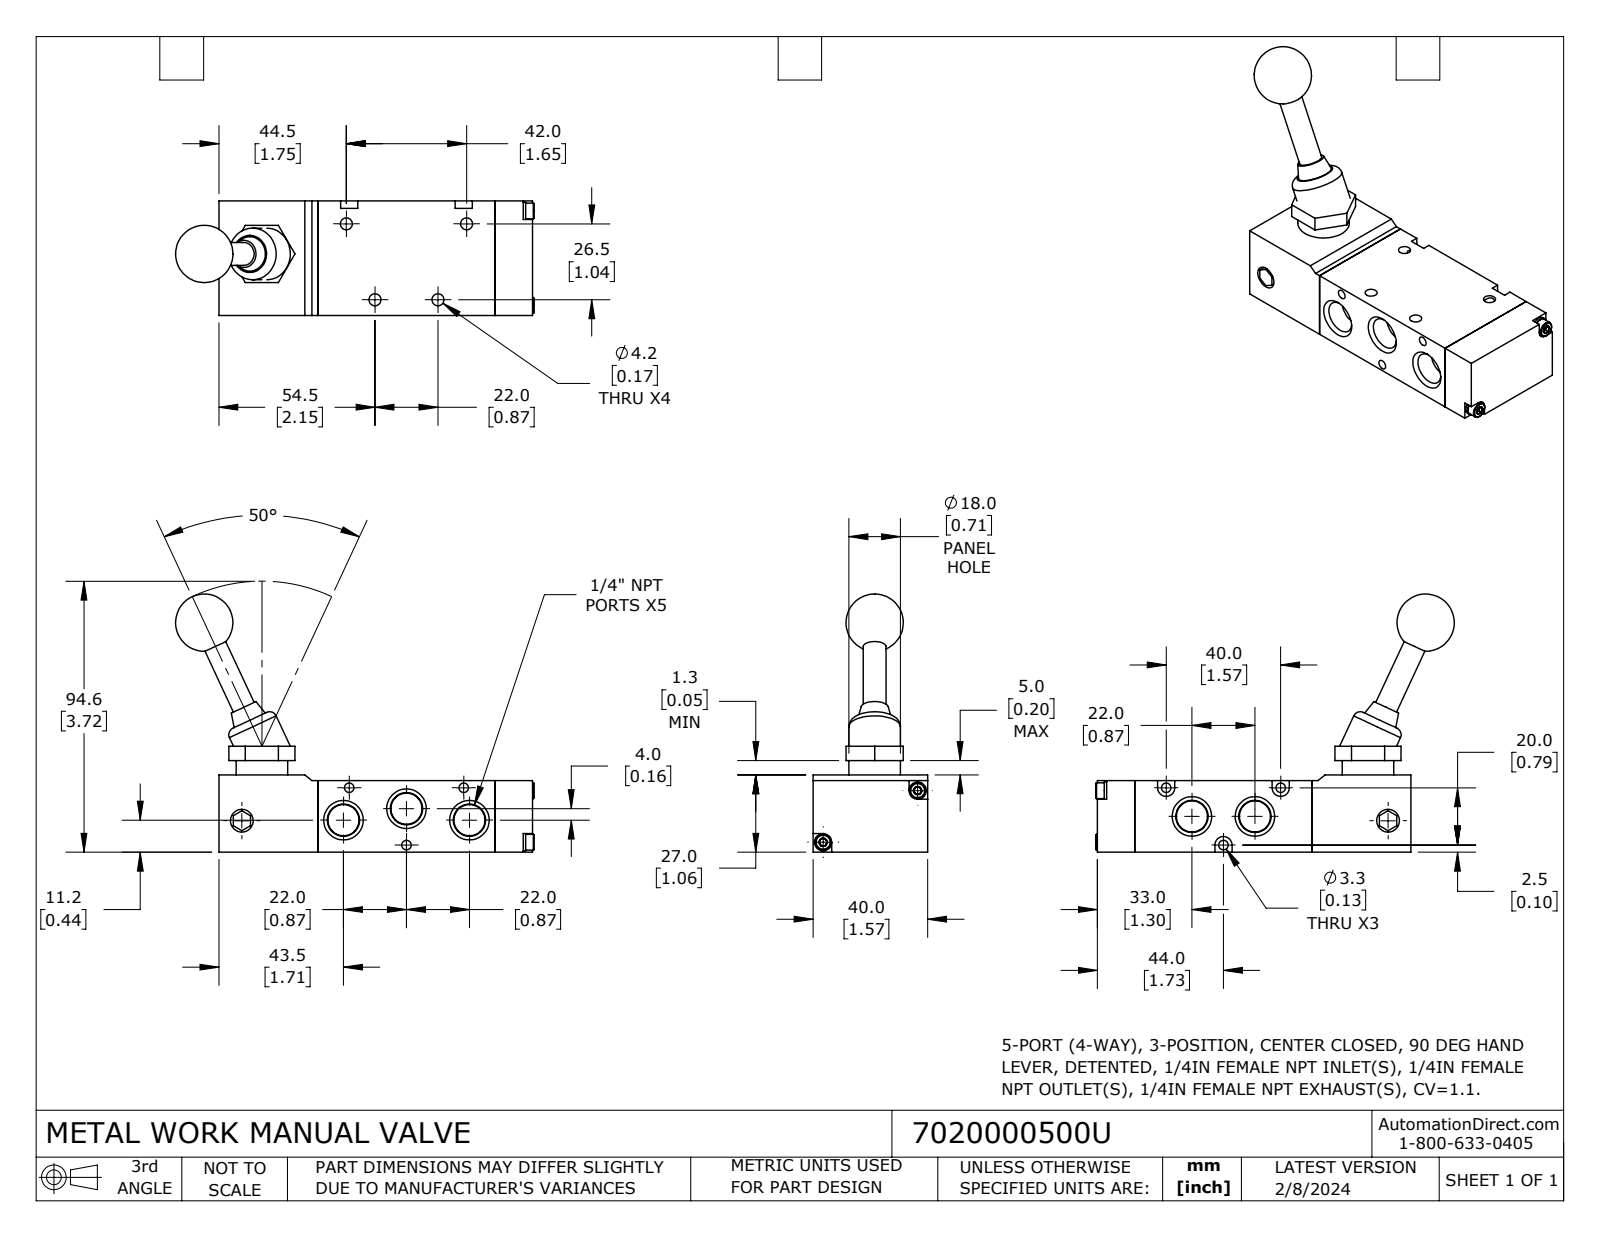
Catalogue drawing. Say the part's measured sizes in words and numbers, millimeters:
The part is named "7020000500U". Its 3-D file was written by "SolidWorks 2023 (CONFIG_CONTROL_DESIGN)". It is 8 solids with 206 faces: 101 planar, 51 cylindrical and 54 other. Overall it measures 125.2 by 90.1 by 40 millimeters. Its volume is 117 900 cubic millimeters and its surface area 28 730 square millimeters. Round holes: 4 of diameter 4.2, 3 of diameter 3.3, 2 of diameter 3, 1 of diameter 8. Round bosses or shafts: 2 of diameter 18, 2 of diameter 6, 2 of diameter 5.5, 1 of diameter 8. Partial cylindrical surfaces (rounded edges, fillets, slot ends): 3 of radius 3. The main face-to-face distances are 25, 40, 62, 96.5, 34.5, 27, 2, 13, 75, 109.5. The hole center spacings are 28.3, 28.3, 41.6, 22, 37.6, 39.2, 40, 42.
